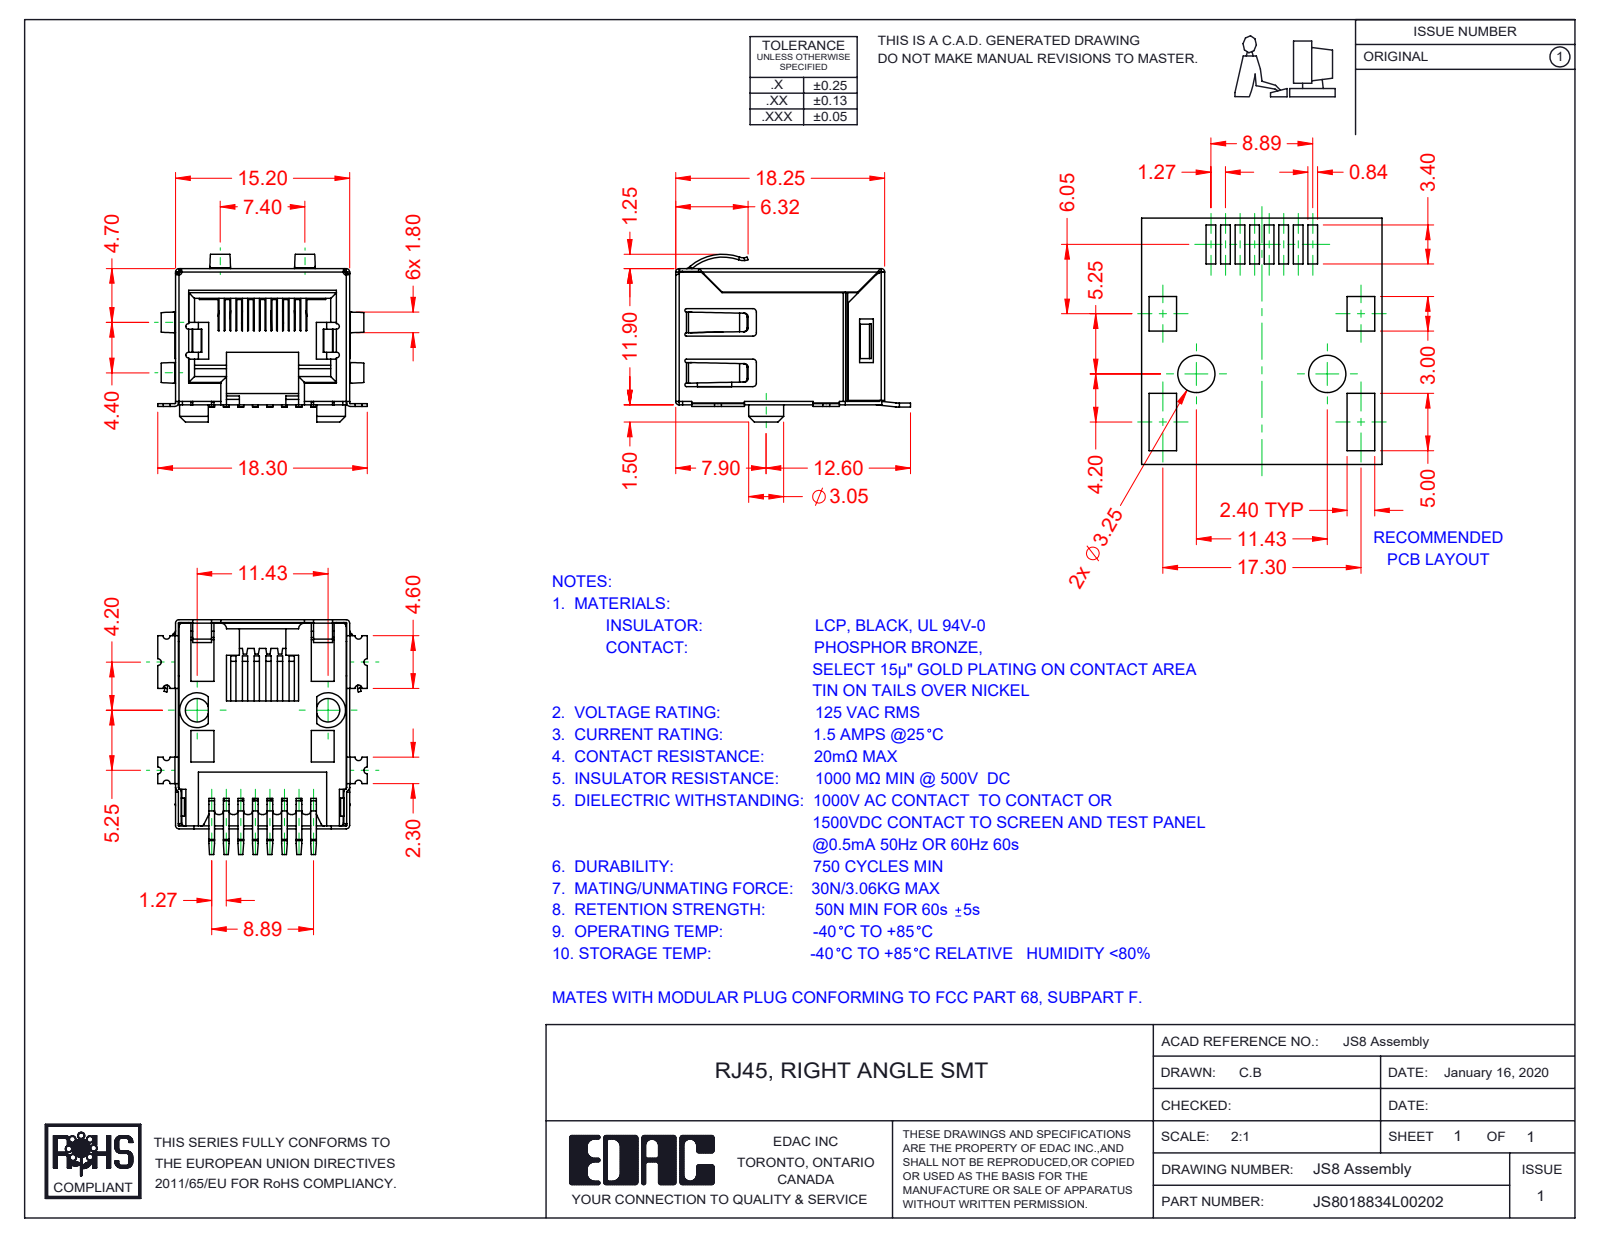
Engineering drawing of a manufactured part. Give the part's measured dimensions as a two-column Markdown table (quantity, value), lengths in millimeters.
| quantity | value |
| --- | --- |
| part name | S8 Shield; S8 Insulator; RJS8018834L00202; S8 Contacts |
| STEP written by | SolidWorks 2016 (CONFIG_CONTROL_DESIGN) |
| units | millimeters |
| bodies | 10 solids, 976 faces (602 planar, 314 cylindrical, 60 other) |
| overall size | 20.5 × 18.3 × 14.65 |
| volume | 1 308 mm³ |
| surface area | 4 634 mm² |
| partial cylindrical surfaces (radius × count) | 0.3 × 59, 0.25 × 19, 0.5 × 18, 0.2 × 17, 0.15 × 8, 0.75 × 7, 1 × 4, 1.25 × 3 |
| main face-to-face distances | 14.65, 14.95, 14.9, 1, 0.35, 14.7, 0.75, 10.9, 1.1, 15.2 |
